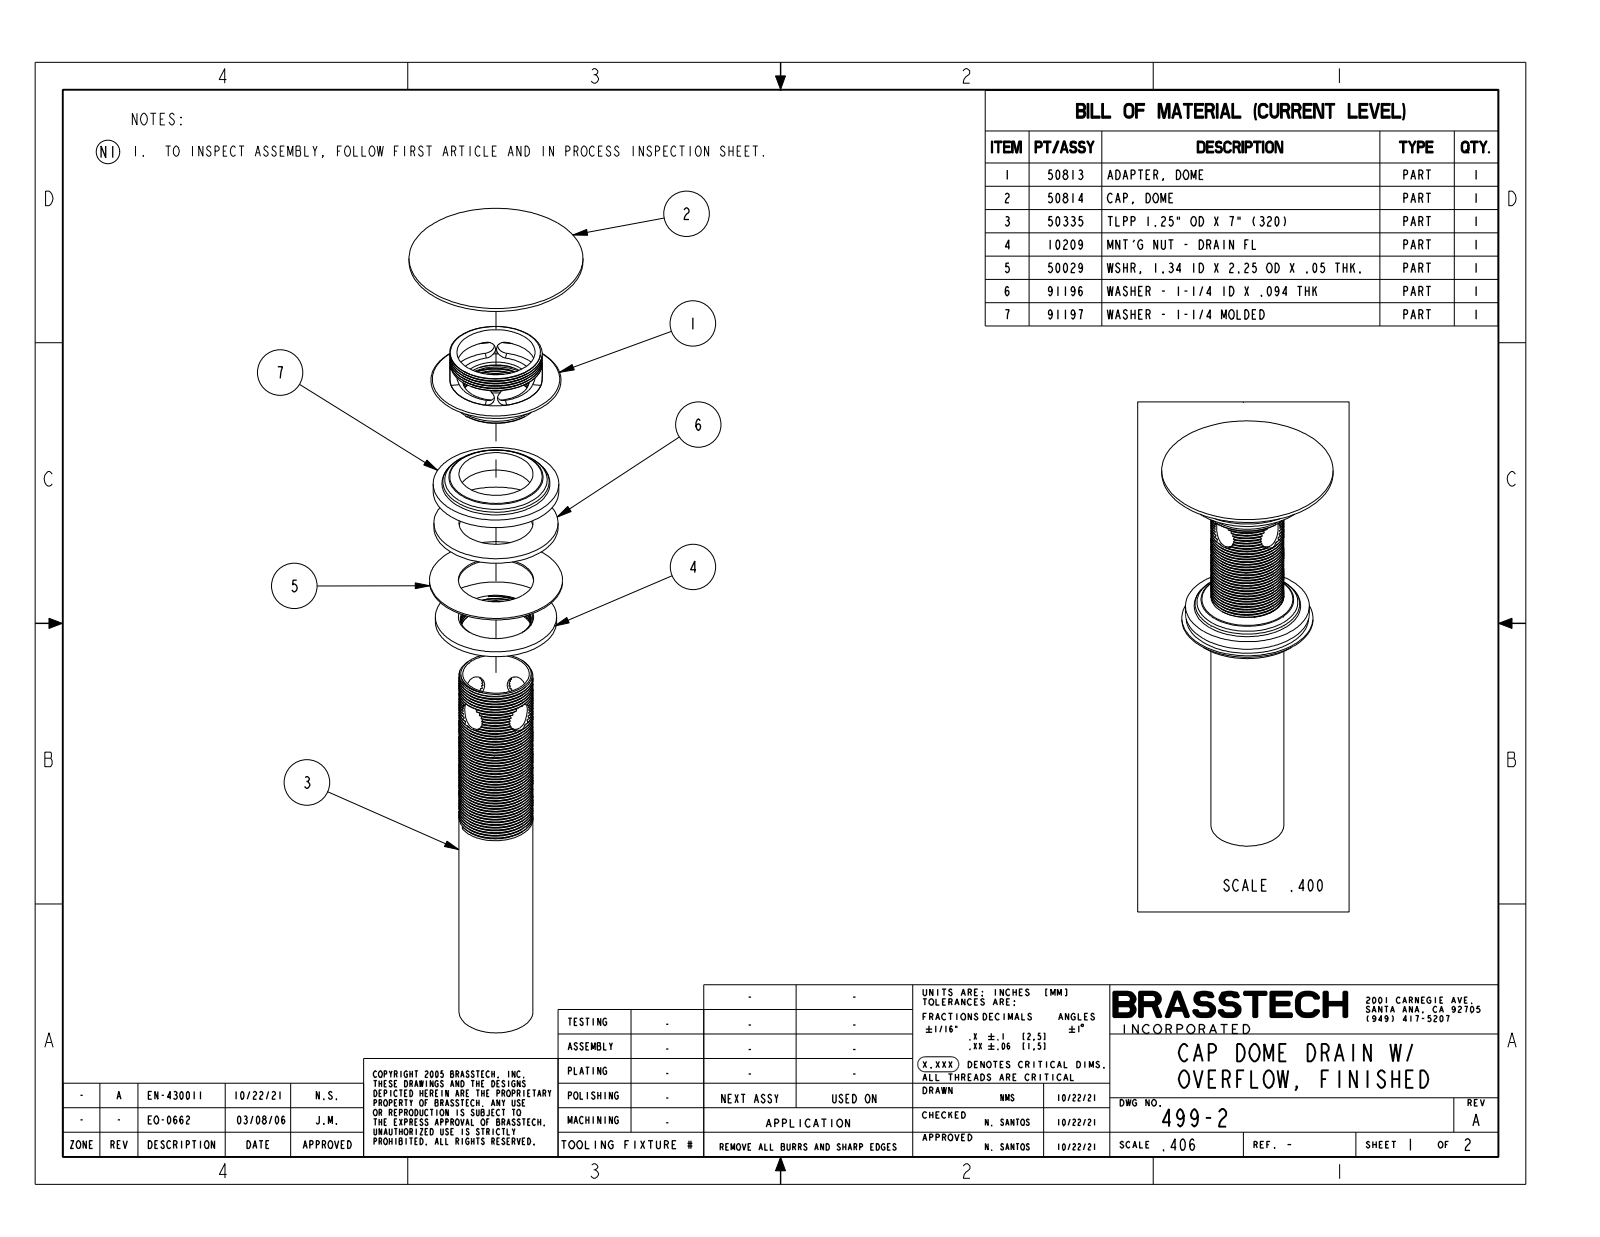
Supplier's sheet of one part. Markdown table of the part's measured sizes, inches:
| quantity | value |
| --- | --- |
| part name | 499-2 |
| STEP written by | CREO PARAMETRIC BY PTC INC, 2018500 (CONFIG_CONTROL_DESIGN) |
| units | inches |
| bodies | 5 solids, 588 faces (40 planar, 336 cylindrical, 212 other) |
| overall size | 7.863 × 2.94 × 2.94 |
| volume | 7.253 in³ |
| surface area | 166.8 in² |
| round holes (diameter × count) | 0.477 × 2, 1.12 × 1, 1.123 × 1, 1.19 × 1, 1.27 × 1, 1.32 × 1, 1.516 × 1, 1.57 × 1 |
| round bosses / shafts (diameter × count) | 2.94 × 1, 2.25 × 1, 2.125 × 1, 2.1 × 1, 2.05 × 1, 1.812 × 1, 1.563 × 1, 1.501 × 1 |
| partial cylindrical surfaces (radius × count) | 0.156 × 8, 0.13 × 6, 0.751 × 1 |
| main face-to-face distances | 0.25, 0.624, 0.28, 0.344, 2.6, 0.1, 2.5, 0.374, 0.35, 0.38 |
